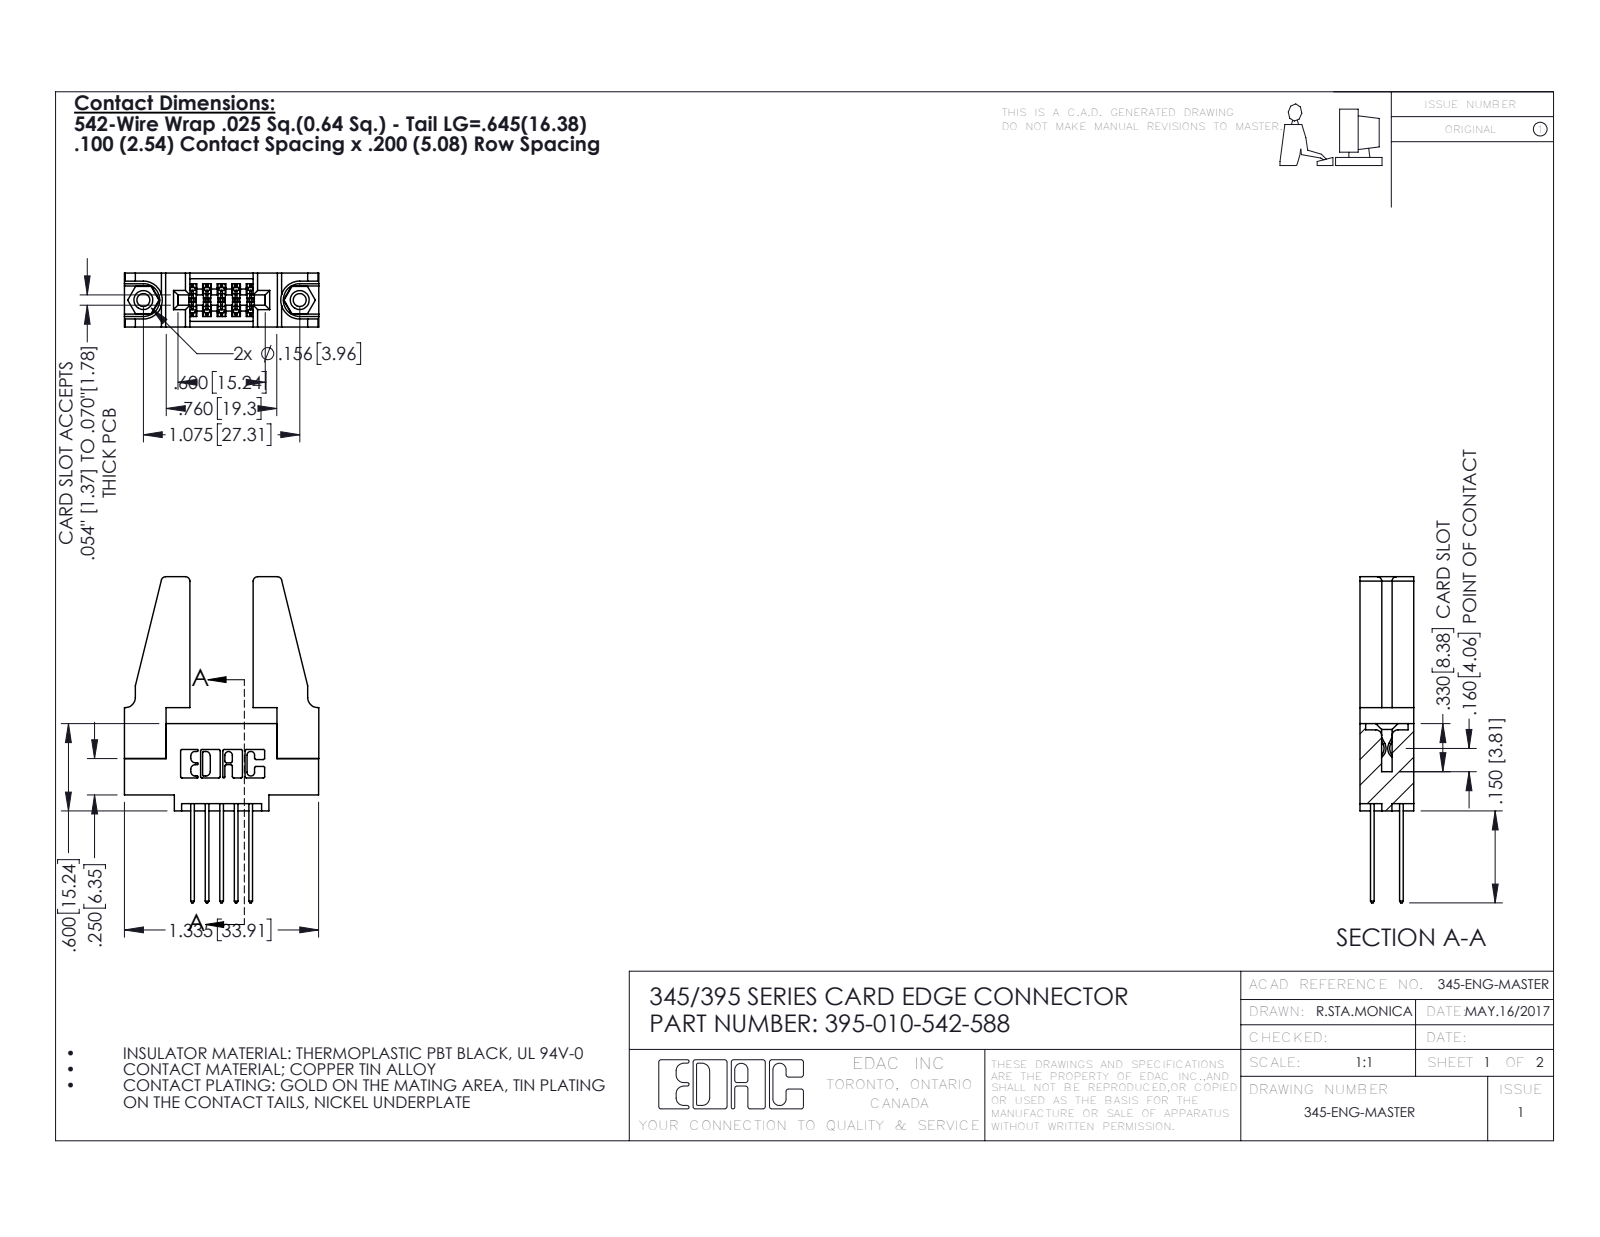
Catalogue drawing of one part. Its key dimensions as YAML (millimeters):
part_name: "345 Part_0.110 Offset - 0.156 Dia-TH; 345-220-078_345-220-088; 395-010-542-588; 345-292-001_345-293-142 (+1 more)"
step_written_by: "SolidWorks 2016 (CONFIG_CONTROL_DESIGN)"
units: millimeters
bodies: {solids: 15, faces: 754, planar: 486, cylindrical: 252, other: 16}
overall_size: [56.9, 33.9, 9.4]
volume: 6180
surface_area: 7039
round_holes:
  - {diameter: 2.3, count: 2}
  - {diameter: 3.2, count: 2}
  - {diameter: 4, count: 2}
  - {diameter: 1.6, count: 1}
round_bosses_or_shafts:
  - {diameter: 3.9, count: 2}
partial_cylinders:
  - {radius: 0.3, count: 22}
  - {radius: 0.2, count: 15}
  - {radius: 0.3, count: 10}
  - {radius: 0.8, count: 8}
  - {radius: 0.2, count: 6}
  - {radius: 0.8, count: 6}
  - {radius: 0.7, count: 3}
  - {radius: 0.4, count: 2}
face_to_face_distances: [9.4, 1.8, 7.6, 5.1, 2.5, 6.9, 0.6, 5.7, 3.8, 3.8]
hole_center_spacings: [6.9, 21.5, 27.3]
